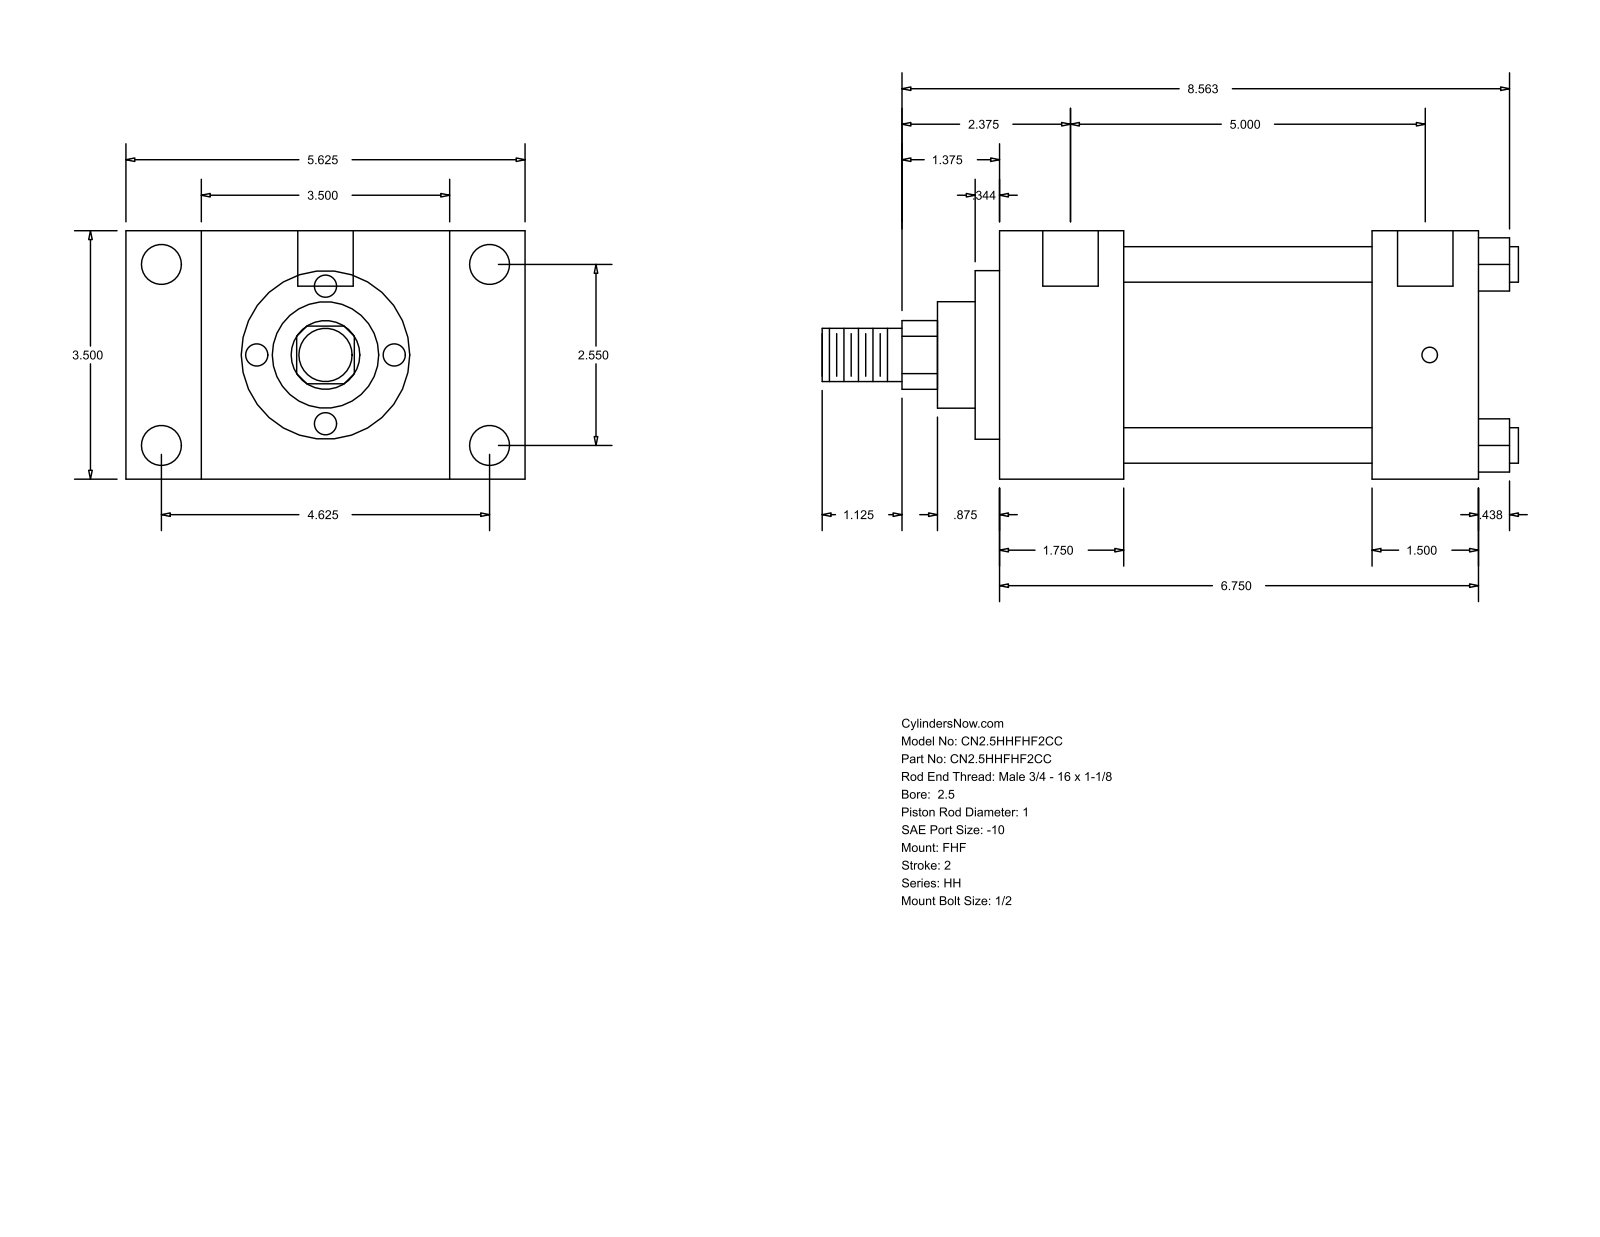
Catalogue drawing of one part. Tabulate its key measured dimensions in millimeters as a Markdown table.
| quantity | value |
| --- | --- |
| part name | HH_FHF__0250_1 |
| STEP written by | GSSL Pune (CONFIG_CONTROL_DESIGN) |
| units | millimeters |
| bodies | 0 solids, 90 faces (61 planar, 29 cylindrical, 0 other) |
| overall size | 249.24 × 142.88 × 88.9 |
| round holes (diameter × count) | 5.56 × 4, 14.3 × 4, 19.84 × 2 |
| round bosses / shafts (diameter × count) | 12.7 × 4, 73.03 × 1, 60.33 × 1, 38.1 × 1, 25.4 × 1, 19.05 × 1 |
| partial cylindrical surfaces (radius × count) | 12.29 × 1 |
| main face-to-face distances | 88.9, 44.46, 26.99, 115.89, 171.46, 127, 142.88, 38.1, 133.36, 8.73 |
| hole center spacings | 1.59, 64.76, 117.48, 128.58, 130.17, 134.15, 126.99 |
